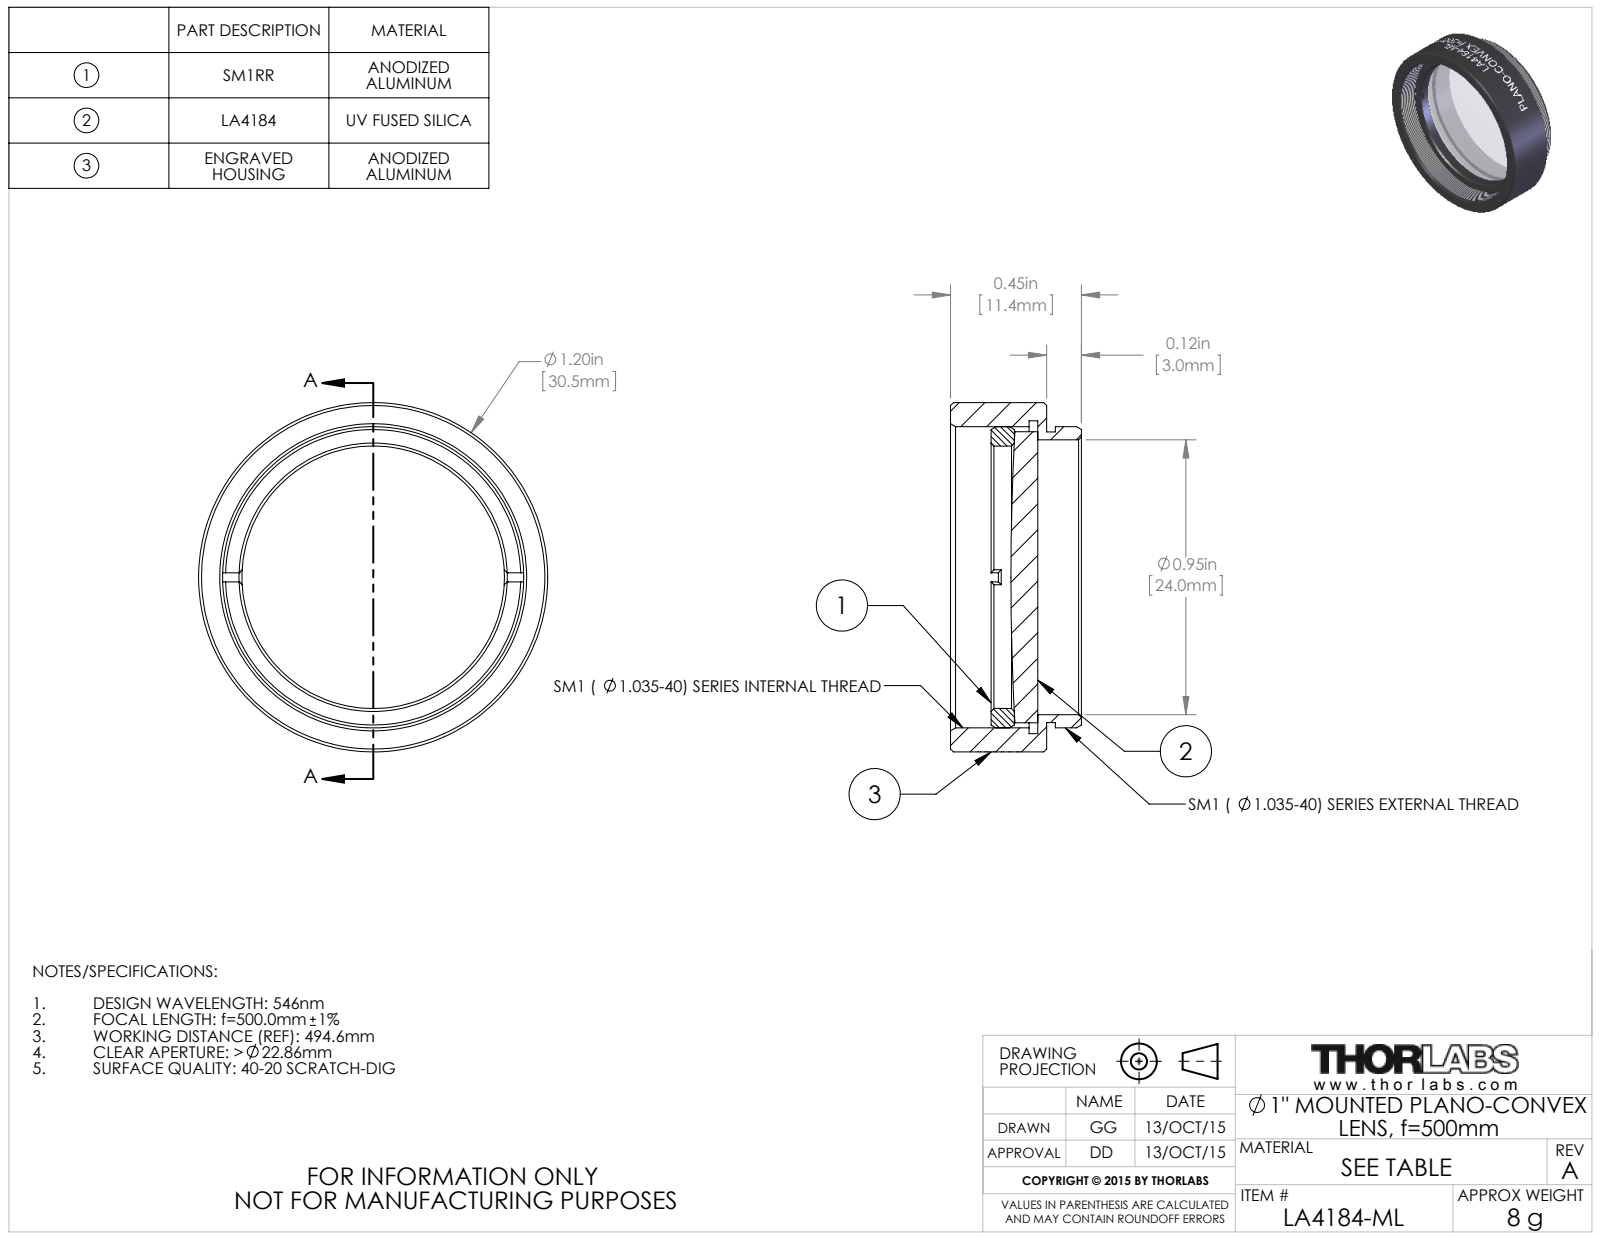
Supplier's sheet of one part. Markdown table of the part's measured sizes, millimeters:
| quantity | value |
| --- | --- |
| part name | TTN039195-E0W |
| STEP written by | SolidWorks 2014 (CONFIG_CONTROL_DESIGN) |
| units | millimeters |
| bodies | 3 solids, 124 faces (20 planar, 80 cylindrical, 24 other) |
| overall size | 30.48 × 30.48 × 11.43 |
| volume | 3 183 mm³ |
| surface area | 4 313 mm² |
| round holes (diameter × count) | 22.91 × 1, 24 × 1, 27.31 × 1 |
| round bosses / shafts (diameter × count) | 30.48 × 1, 26.29 × 1, 25.4 × 1, 25.37 × 1 |
| main face-to-face distances | 0.76, 8.38, 7.62, 2.82, 2.06, 5.56, 4.85, 4.09, 2.03, 3.53 |
